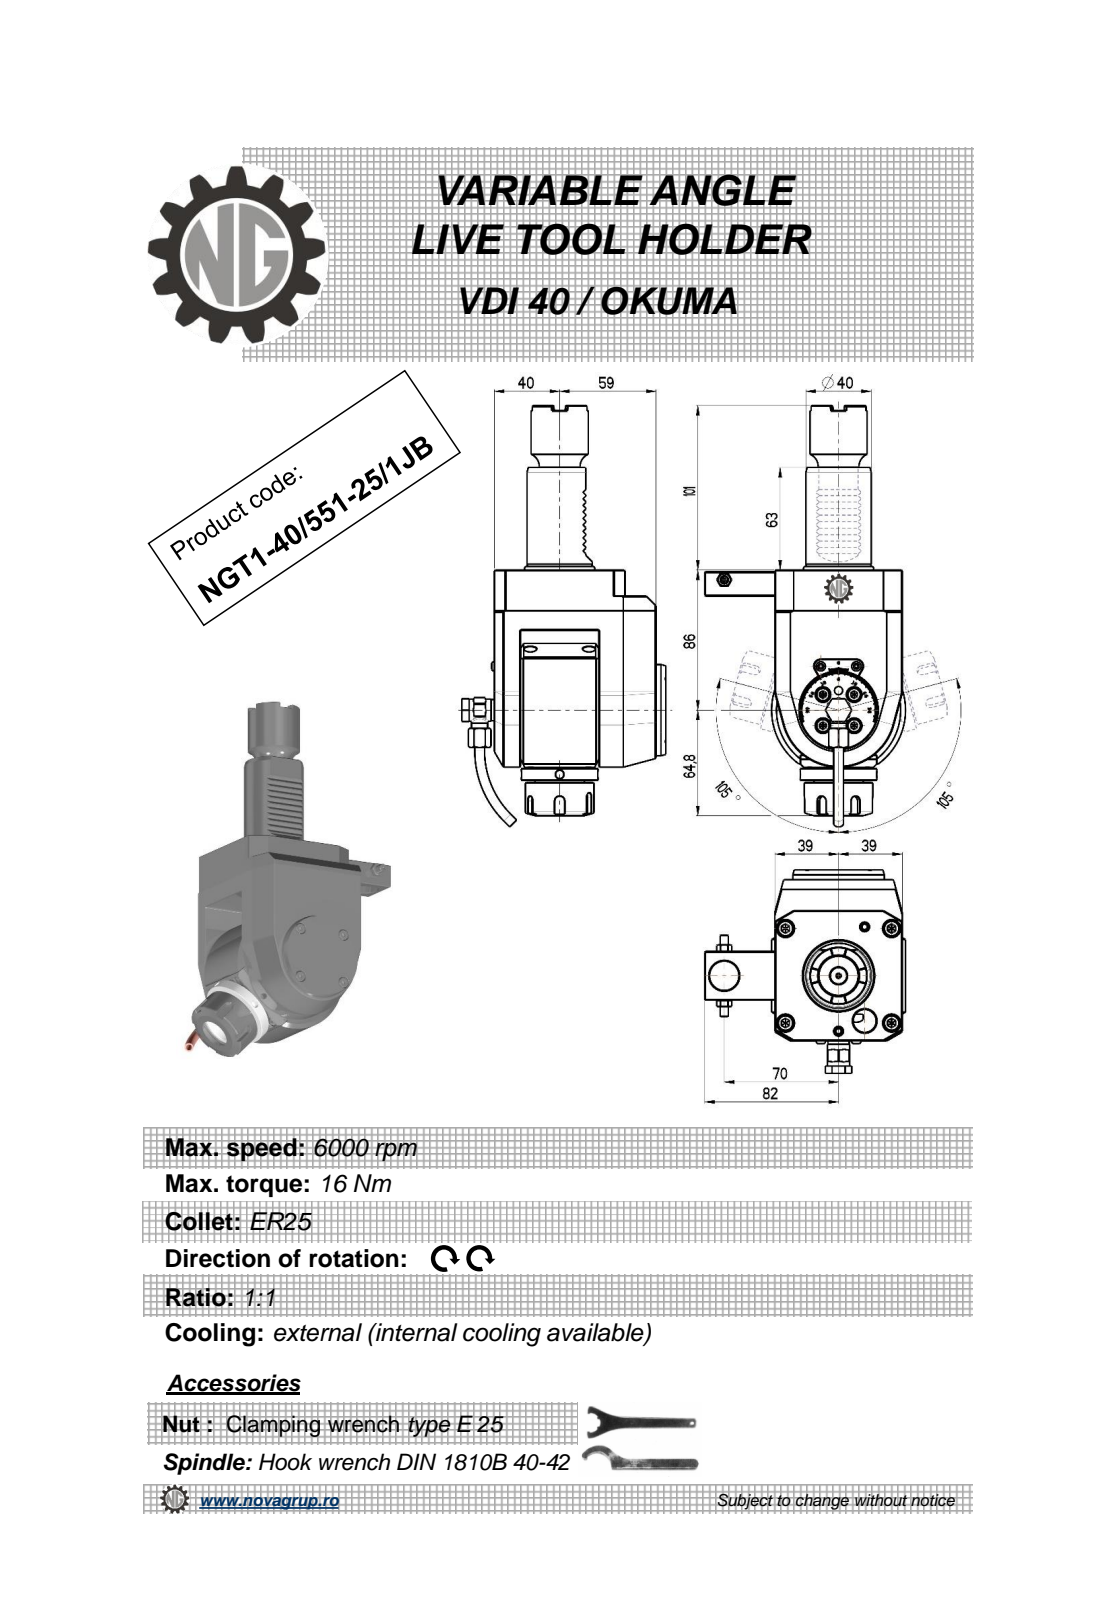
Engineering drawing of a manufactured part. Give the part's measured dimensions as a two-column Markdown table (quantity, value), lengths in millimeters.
| quantity | value |
| --- | --- |
| part name | NGT1_40_551_25_1JB |
| STEP written by | PRO/ENGINEER BY PARAMETRIC TECHNOLOGY CORPORATION, 2010280 (CONFIG_CONTROL_DESIGN) |
| units | millimeters |
| bodies | 1 solid, 609 faces (252 planar, 136 cylindrical, 221 other) |
| overall size | 258.67 × 124.9 × 123 |
| volume | 954 911 mm³ |
| surface area | 89 834 mm² |
| round holes (diameter × count) | 4 × 3, 5 × 2, 3 × 1, 4.2 × 1, 6.2 × 1, 9 × 1, 9.5 × 1, 10 × 1, 11 × 1, 18 × 1, 20.3 × 1, 25 × 1 |
| round bosses / shafts (diameter × count) | 6 × 2, 5.7 × 2, 82 × 1, 56 × 1, 47 × 1, 42 × 1, 40 × 1, 36 × 1 |
| partial cylindrical surfaces (radius × count) | 0.26 × 12, 0.3 × 10, 3 × 5, 0.5 × 4, 1 × 2, 10 × 2, 7.7 × 1, 35 × 1 |
| main face-to-face distances | 16, 37, 64, 99, 78, 6, 105, 1, 21, 25 |
| hole center spacings | 0.4, 39.45, 49, 49.4, 70, 85.45, 85.68, 106.3 |
